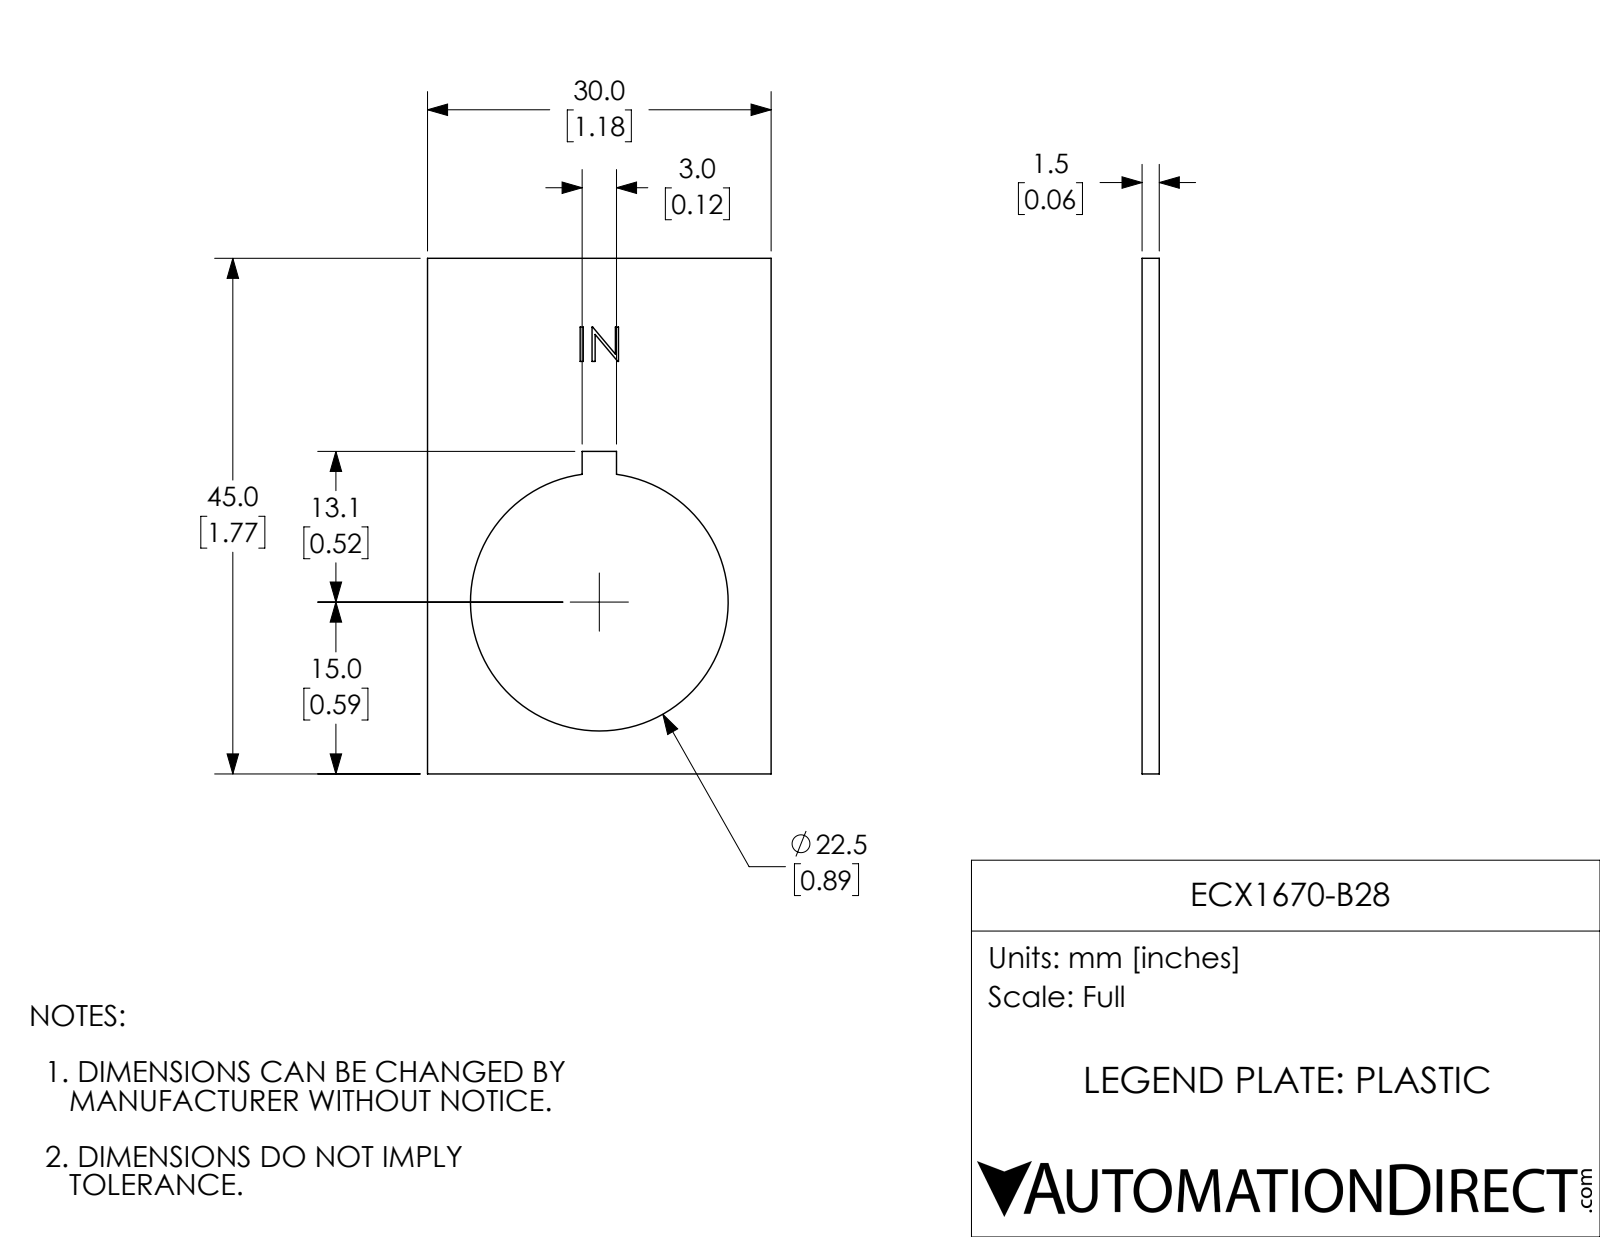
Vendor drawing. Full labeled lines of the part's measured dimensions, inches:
Part name (STEP PRODUCT): ECX1670-B28
STEP written by: SolidWorks 2017 (AUTOMOTIVE_DESIGN)
Units: inches
Bodies: 1 solid, 28 faces (25 planar, 3 cylindrical, 0 other)
Overall size (bounding box): 1.772 × 1.181 × 0.059
Volume: 0.087 in³ · Surface area: 3.458 in²
Round holes (diameter × count): ⌀0.886 ×1
Main face-to-face distances: 0.059, 1.181, 1.772, 0.531, 0.65, 1.108, 0.663, 0.058, 0.118, 0.525
